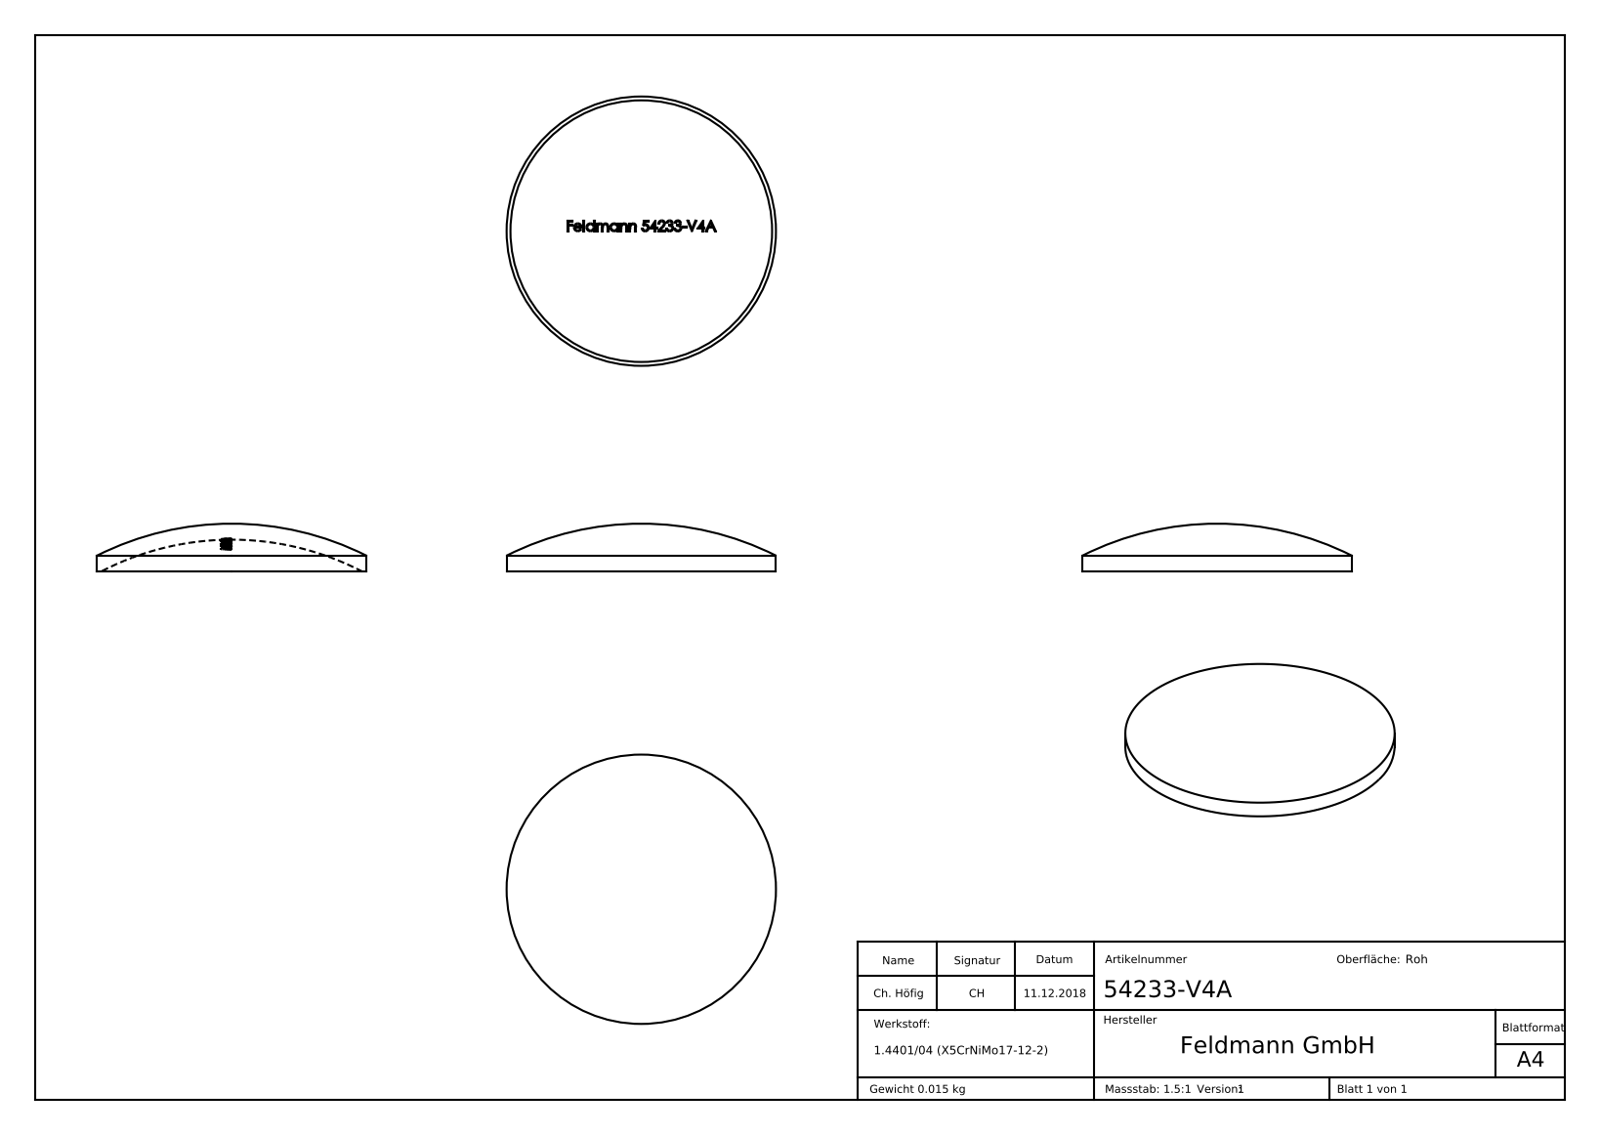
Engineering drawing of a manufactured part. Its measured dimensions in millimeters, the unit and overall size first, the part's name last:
Units: millimetres
Overall size (bounding box): 33.7 × 33.7 × 6
Round bosses / shafts (diameter × count): ⌀33.7 ×1
Main face-to-face distances: 2.97, 0.44, 0.88, 1.26, 0.39, 1.65, 1.32, 2.01, 5.97, 4.92
Volume: 1 884 mm³ · Surface area: 2 106 mm²
Bodies: 1 solid, 253 faces (121 planar, 2 cylindrical, 130 other)
Part name (STEP PRODUCT): 54233-V4A
STEP written by: SolidWorks 2015 (CONFIG_CONTROL_DESIGN)
